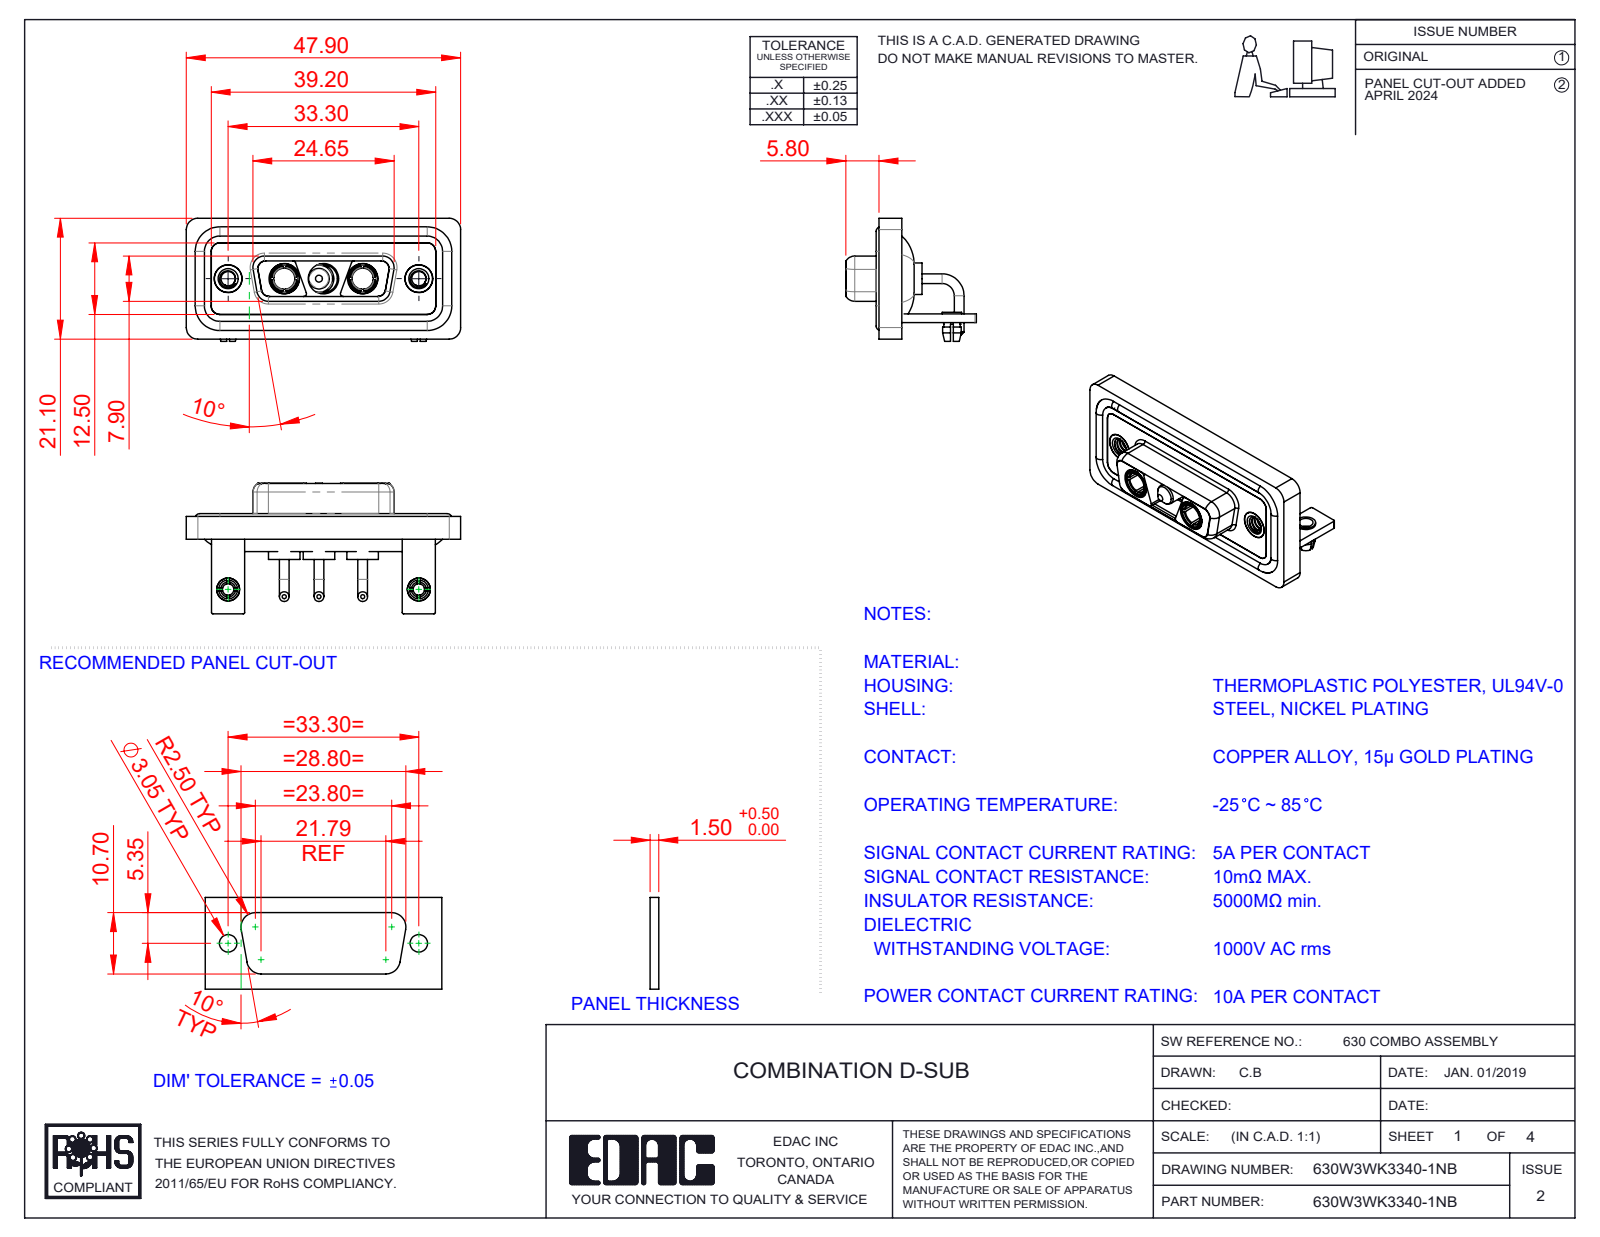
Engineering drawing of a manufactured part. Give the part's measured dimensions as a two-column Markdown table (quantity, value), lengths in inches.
| quantity | value |
| --- | --- |
| part name | Power Socket_10A RA; 630Combo Threaded Rivet_A; 630Combo Shell Rear_15 Contacts; 630Combo Waterproof Housing_15 Contacts (+6 more) |
| STEP written by | SolidWorks 2023 (CONFIG_CONTROL_DESIGN) |
| units | inches |
| bodies | 17 solids, 729 faces (246 planar, 318 cylindrical, 165 other) |
| overall size | 1.886 × 0.898 × 0.846 |
| volume | 0.382 in³ |
| surface area | 16.33 in² |
| round holes (diameter × count) | 0.191 × 5, 0.098 × 4, 0.209 × 3, 0.079 × 2, 0.126 × 2, 0.146 × 2, 0.157 × 2, 0.159 × 2, 0.197 × 2 |
| round bosses / shafts (diameter × count) | 0.067 × 6, 0.063 × 4, 0.217 × 3, 0.205 × 3, 0.187 × 3, 0.148 × 3, 0.195 × 2, 0.195 × 2 |
| partial cylindrical surfaces (radius × count) | 0.079 × 21, 0.059 × 18, 0.01 × 16, 0.053 × 12, 0.02 × 9, 0.063 × 8, 0.024 × 4, 0.026 × 4 |
| main face-to-face distances | 0.016, 0.114, 0.059, 0.146, 0.071, 0.043, 0.161, 0.063, 0.098, 0.055 |
| hole center spacings | 0.27, 0.386, 0.656, 0.925, 1.311, 0.539 |
